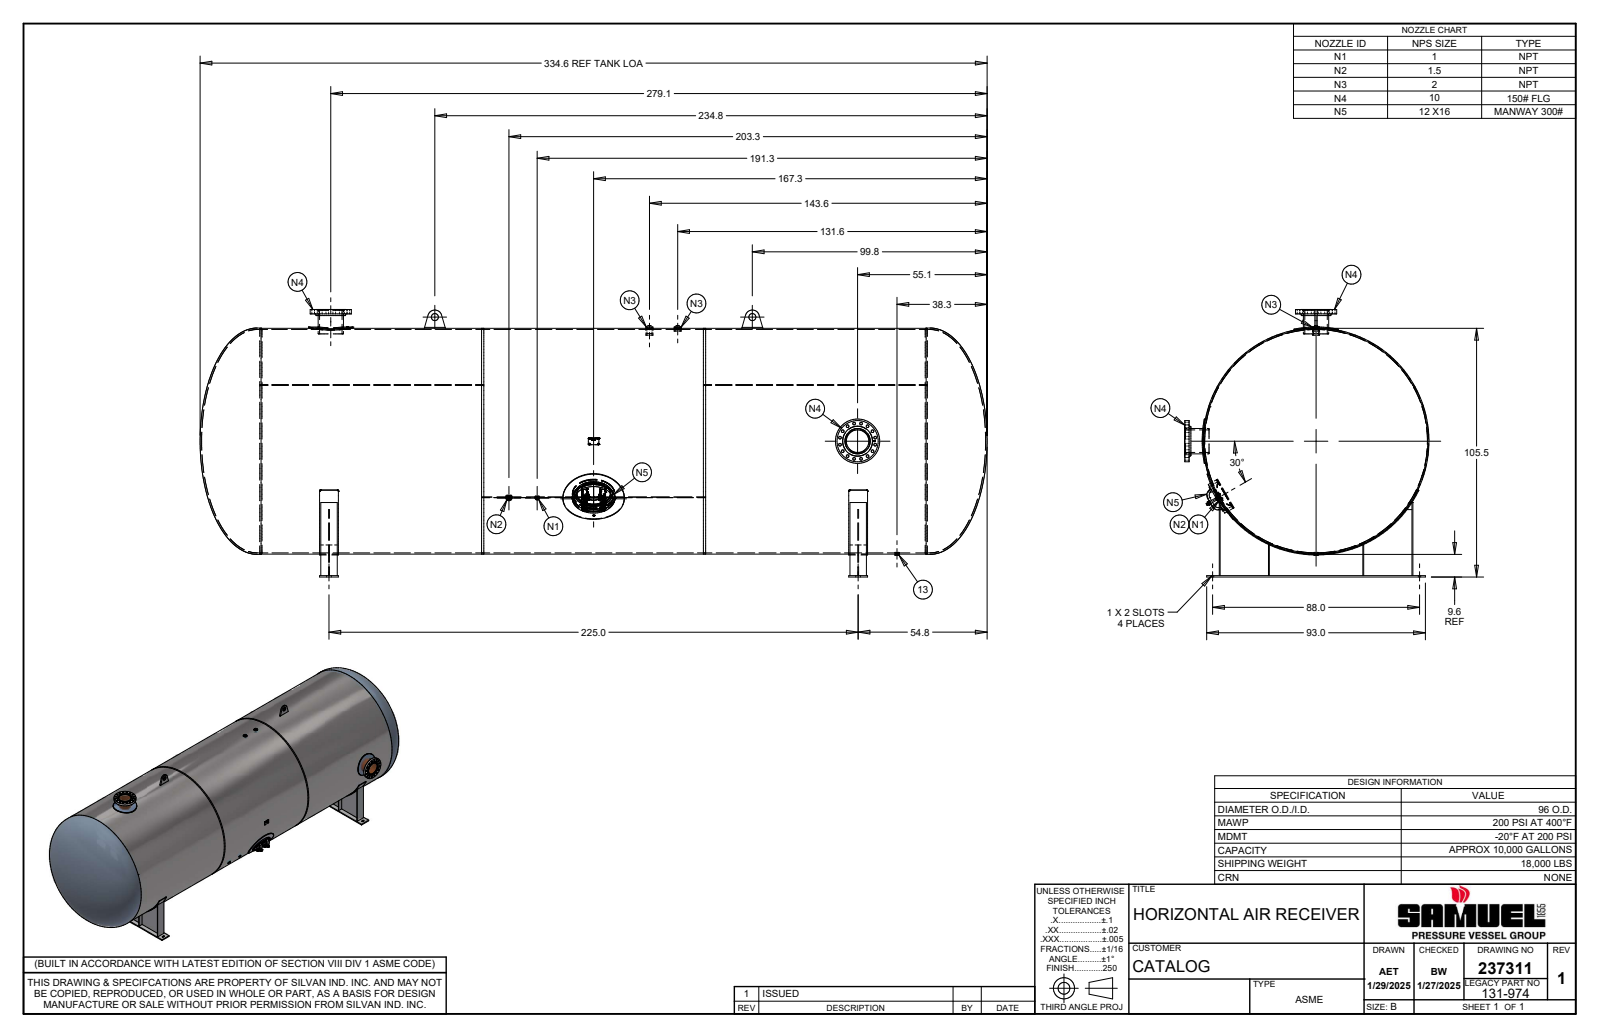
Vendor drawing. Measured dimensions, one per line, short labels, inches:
name: 237311; 131-974SF-SL1; 131-974SF-SL2; 131-974SF-SL3 (+8 more)
written by: Autodesk Inventor 2022 (AUTOMOTIVE_DESIGN)
unit: in
bodies: 49 solids, 1026 faces (516 planar, 224 cylindrical, 286 other)
size: 334.625 × 113.497 × 103.875
volume: 60 184 in³; area: 234 163 in²
holes: 34× ⌀1.125, 2× ⌀0.42, 2× ⌀0.865, 2× ⌀1, 2× ⌀1.193, 2× ⌀2, 2× ⌀3, 2× ⌀9.562, 2× ⌀10, 2× ⌀10.7, 2× ⌀10.75, 1× ⌀0.422
bosses: 2× ⌀18.813, 2× ⌀17.5, 2× ⌀12.75, 2× ⌀12.625, 2× ⌀3, 2× ⌀1.75, 2× ⌀1, 1× ⌀95.75
rounds: 16× R0.5, 12× R0.776, 6× R0.375, 6× R1, 5× R3, 4× R0.75, 4× R1.156, 3× R2.776
face distances: 225, 0.375, 0.625, 225.375, 224.625, 0.375, 81.937, 20.906, 61.031, 94.313
hole spacings: 5.836, 7.625, 8.472, 12.68, 2.975, 10.783, 14.089, 14.957
